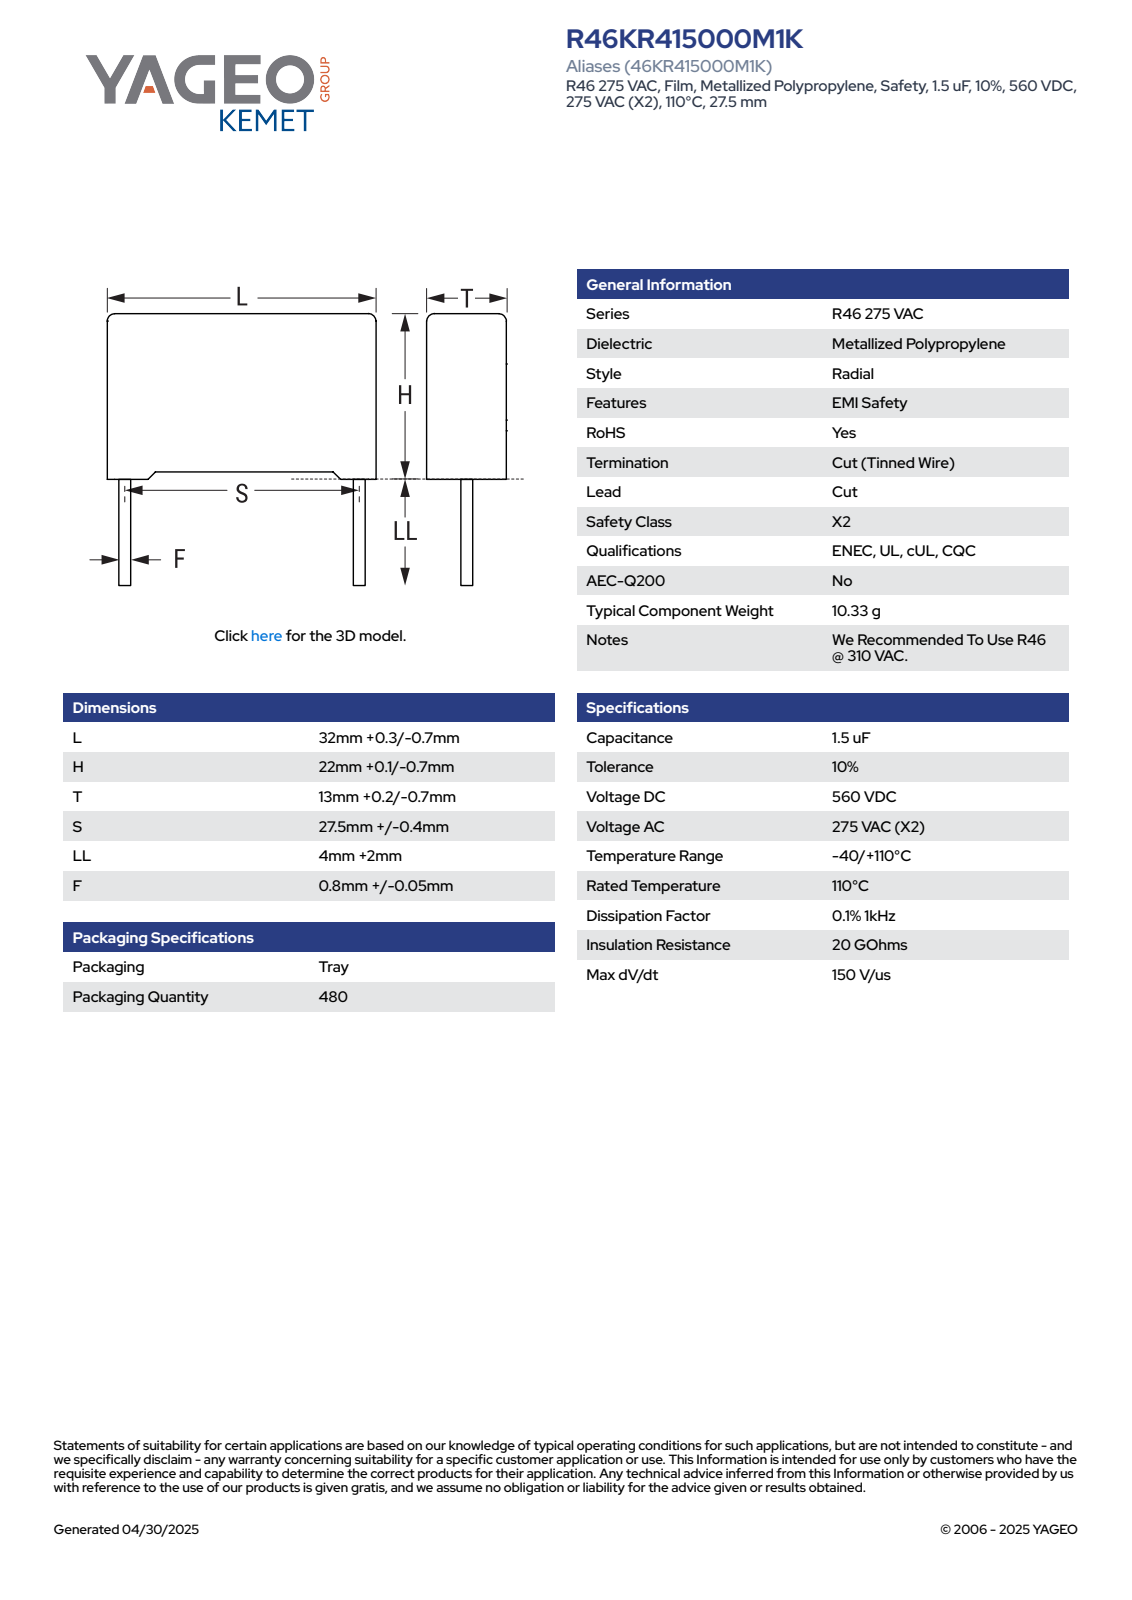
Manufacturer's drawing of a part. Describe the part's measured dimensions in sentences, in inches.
The part is named "CFR_RB2_32X22X13_L32.3H22.1T13.2S27.5LL6F0.85". Its 3-D file was written by "SolidWorks 2021 (AUTOMOTIVE_DESIGN)". It is 4 solids with 85 faces: 77 planar, 8 cylindrical and 0 other. Overall it measures 1.272 by 1.106 by 0.52 inches. Its volume is 0.557 cubic inches and its surface area 4.573 square inches. Round bosses or shafts: 2 of diameter 0.033. Partial cylindrical surfaces (rounded edges, fillets, slot ends): 4 of radius 0.02. The main face-to-face distances are 0.52, 0.84, 1.272, 0.841, 0.03, 0.03, 0.87, 0.043, 0.52, 1.229.
